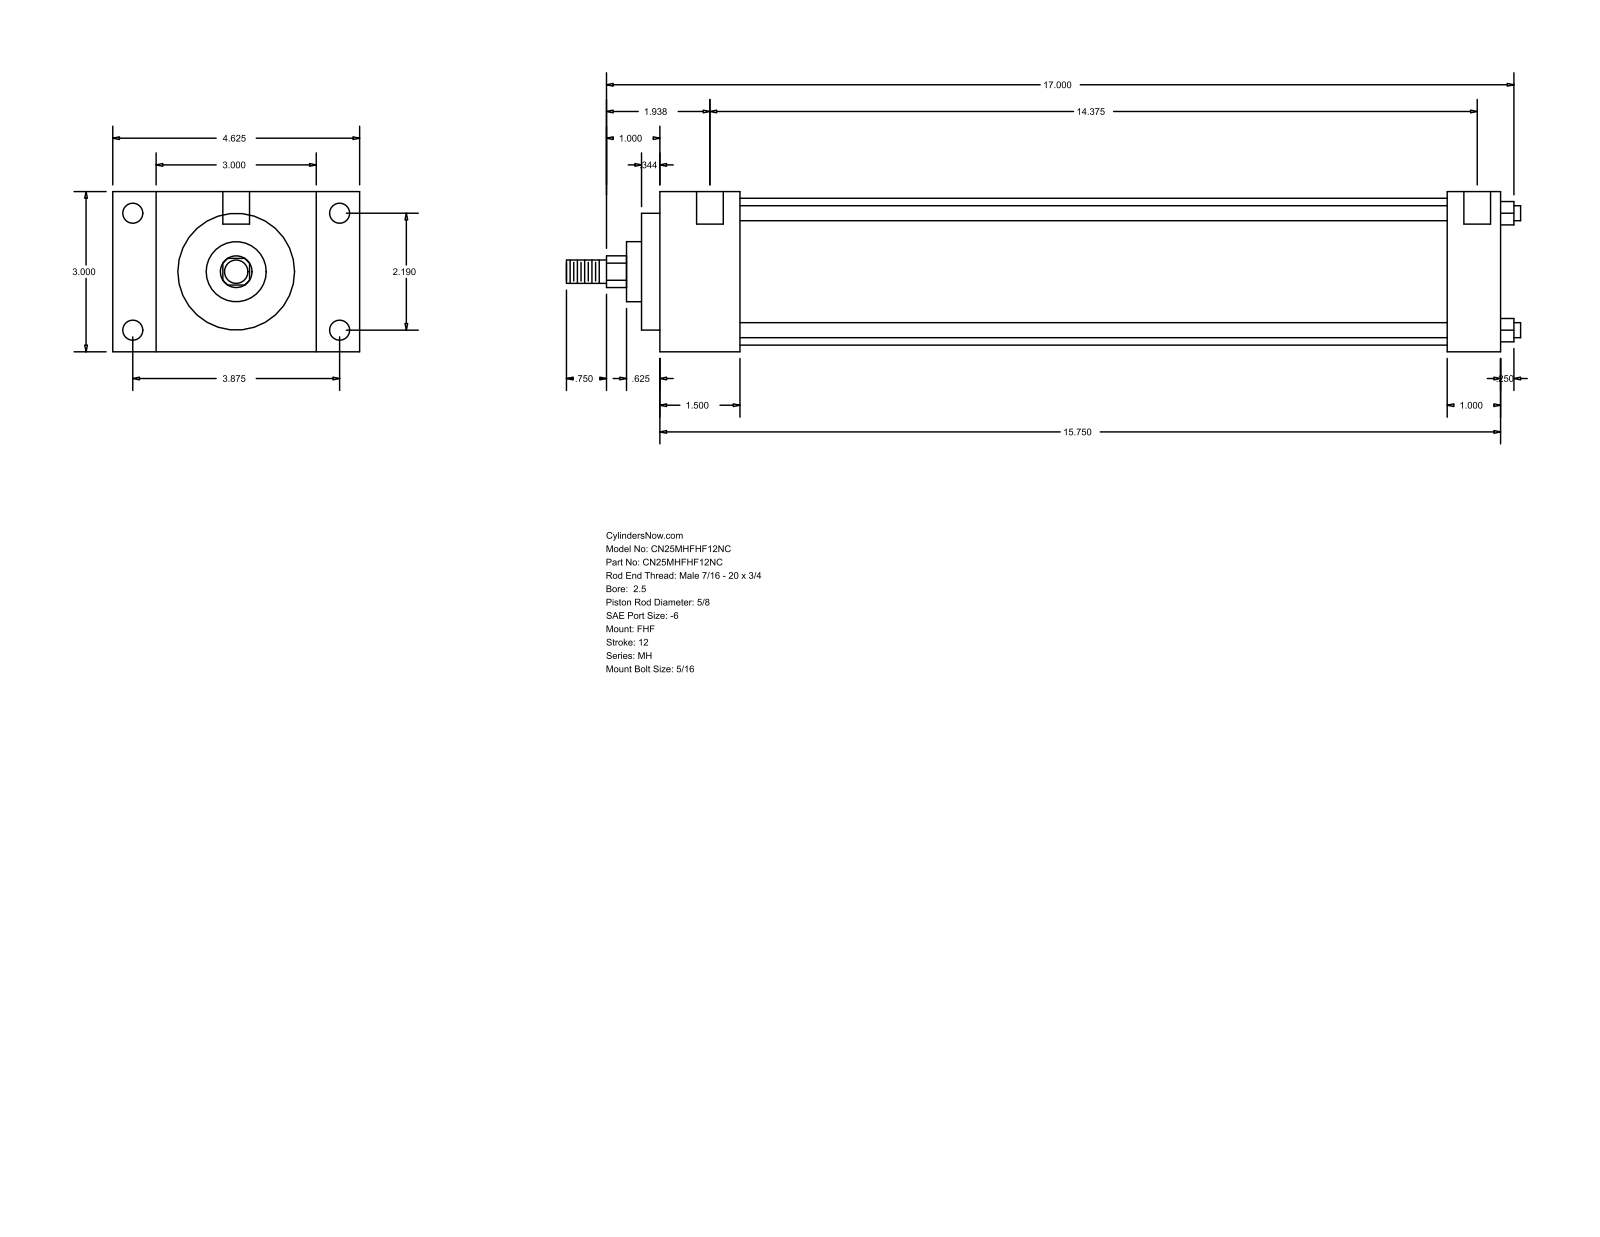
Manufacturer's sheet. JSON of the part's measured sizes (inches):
{"part_name": "MH_FHF__0250_0.625", "step_written_by": "GSSL Pune (CONFIG_CONTROL_DESIGN)", "units": "inches", "bodies": {"solids": 0, "faces": 90, "planar": 61, "cylindrical": 29, "other": 0}, "overall_size": [17.875, 4.625, 3], "round_holes": [[0.219, 4], [0.375, 4], [0.5, 2]], "round_bosses_or_shafts": [[0.281, 4], [2.75, 1], [2.187, 1], [1.125, 1], [0.625, 1], [0.437, 1]], "partial_cylinders_radius": [[0.297, 1]], "face_to_face_distances": [3, 15.75, 1.5, 14.25, 0.813, 3.813, 4.625, 1, 14.75, 13.25], "hole_center_spacings": [2.19, 3.875, 4.451, 14.687, 0.125, 0.187, 14.375, 14.5]}
